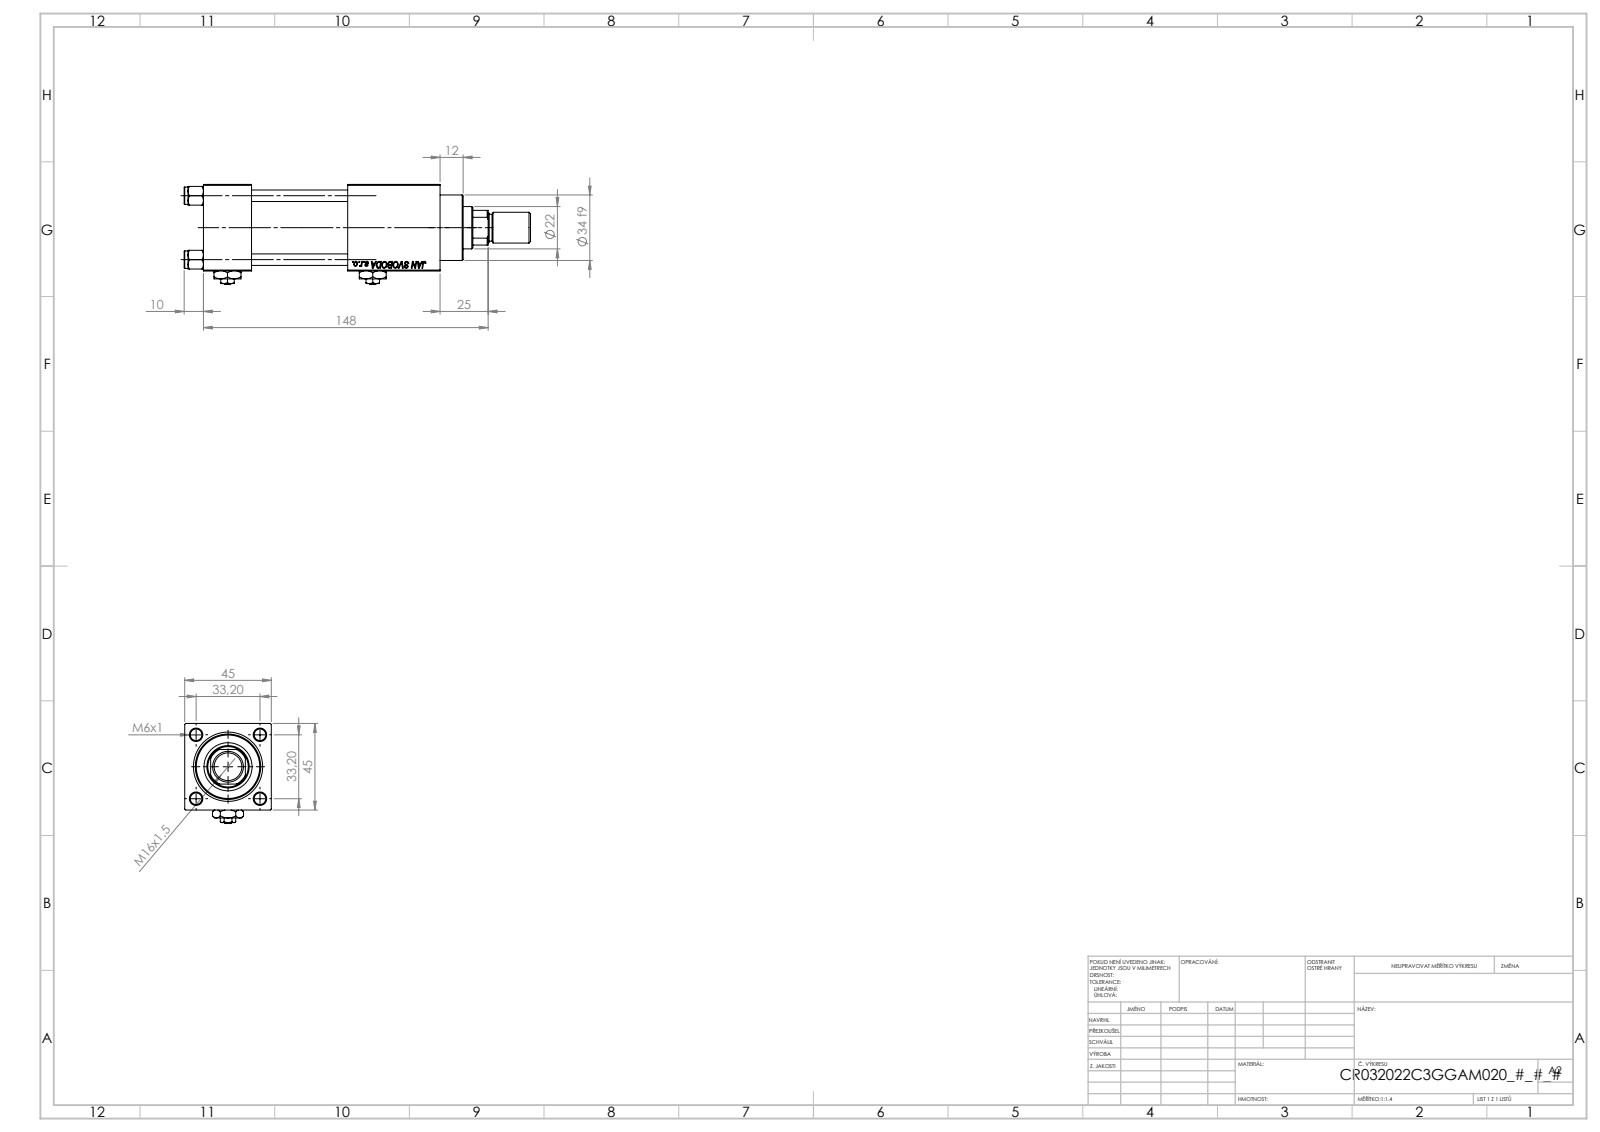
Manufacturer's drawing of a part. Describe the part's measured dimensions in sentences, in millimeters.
The part is named "V215CR_C_TYCINKA; Zatka_pro_OIL_PORT; V215_VC_A; ROD_END_AH (+3 more)". Its 3-D file was written by "SolidWorks 2019 (CONFIG_CONTROL_DESIGN)". It is 14 solids with 1262 faces: 576 planar, 102 cylindrical and 584 other. Overall it measures 180 by 52 by 45 millimeters. Its volume is 212 213 cubic millimeters and its surface area 74 748 square millimeters. Round holes: 4 of diameter 6, 2 of diameter 7, 2 of diameter 13.16, 2 of diameter 20, 1 of diameter 10.5, 1 of diameter 22, 1 of diameter 24, 1 of diameter 25, 1 of diameter 32, 1 of diameter 33. Round bosses or shafts: 4 of diameter 9, 1 of diameter 38, 1 of diameter 34, 1 of diameter 16, 1 of diameter 14. Partial cylindrical surfaces (rounded edges, fillets, slot ends): 1 of radius 10.5. The main face-to-face distances are 45, 25, 123, 50, 75, 98, 44.8, 48, 94.3, 69.3. The hole center spacings are 23.48, 33.2, 46.95, 75.5.
